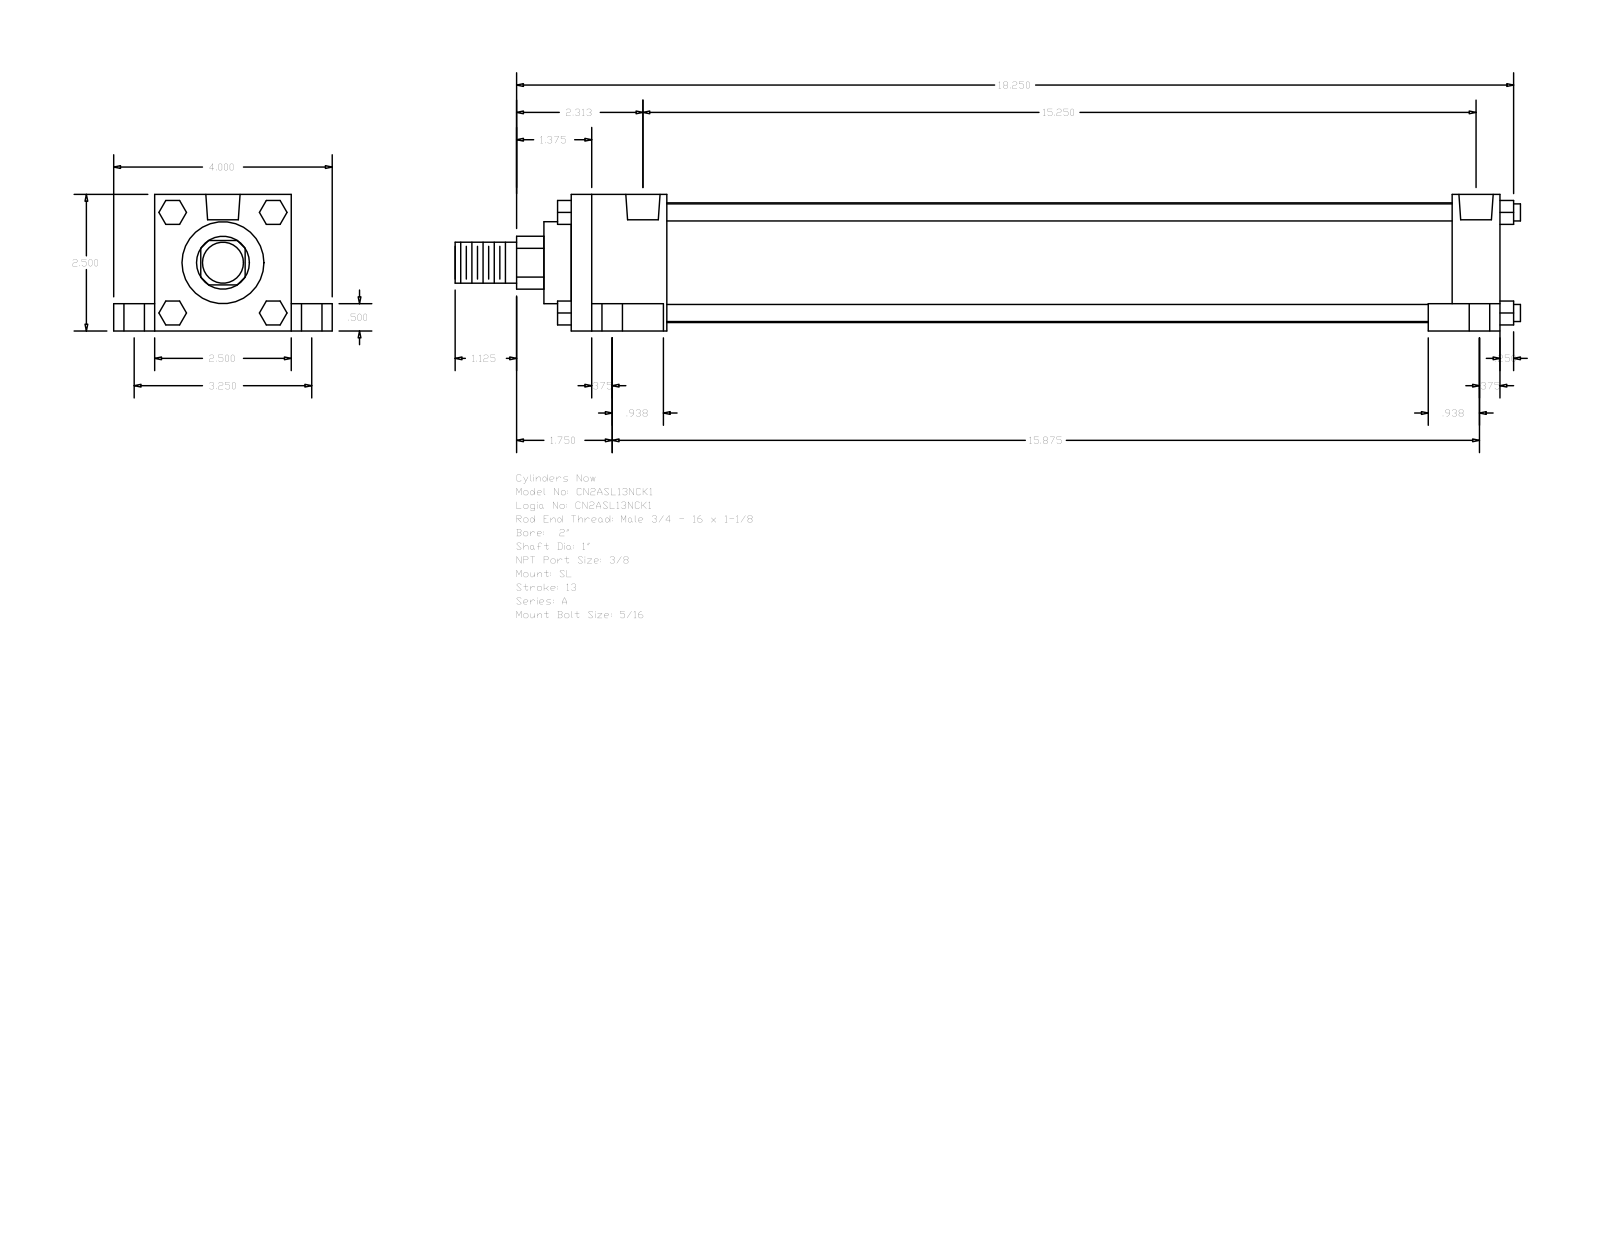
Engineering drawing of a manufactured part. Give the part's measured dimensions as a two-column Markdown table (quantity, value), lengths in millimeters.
| quantity | value |
| --- | --- |
| part name | A_SL__0200_1 |
| STEP written by | GSSL Pune (CONFIG_CONTROL_DESIGN) |
| units | millimeters |
| bodies | 0 solids, 148 faces (112 planar, 36 cylindrical, 0 other) |
| overall size | 495.3 × 101.6 × 63.5 |
| round holes (diameter × count) | 5.56 × 4, 9.53 × 4, 15.88 × 4, 15.93 × 2 |
| round bosses / shafts (diameter × count) | 7.94 × 4, 55.63 × 1, 38.1 × 1, 25.4 × 1, 19.05 × 1 |
| partial cylindrical surfaces (radius × count) | 12.29 × 1 |
| main face-to-face distances | 63.5, 12.7, 431.8, 50.8, 22.22, 19.05, 82.55, 44.45, 387.35, 409.58 |
| hole center spacings | 41.3, 41.64, 43.67, 44.22, 82.54, 381.78, 389.54, 391.12 |
